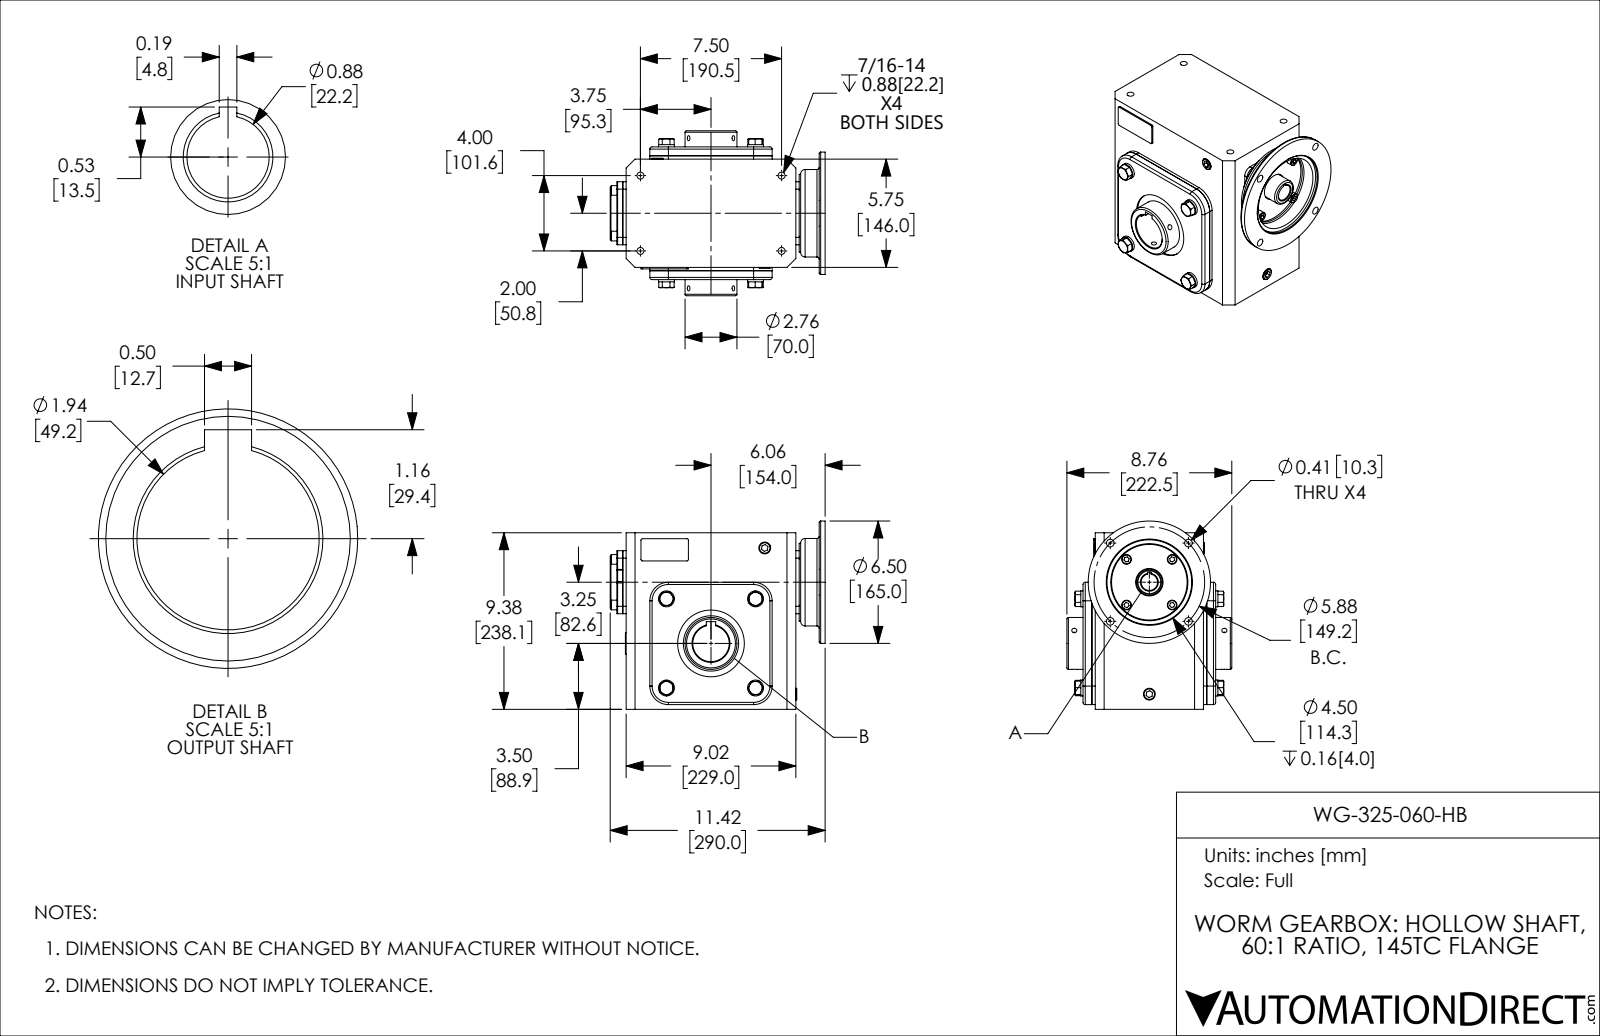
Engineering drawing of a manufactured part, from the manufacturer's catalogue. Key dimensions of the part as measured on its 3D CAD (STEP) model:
Part name (STEP PRODUCT): WG-325-060-HB
STEP written by: SolidWorks 2017 (AUTOMOTIVE_DESIGN)
Units: inches
Bodies: 39 solids, 587 faces (314 planar, 178 cylindrical, 95 other)
Overall size (bounding box): 11.417 × 9.998 × 8.76
Volume: 516.3 in³ · Surface area: 987.3 in²
Round holes (diameter × count): ⌀0.272 ×6, ⌀0.368 ×4, ⌀0.406 ×4, ⌀0.628 ×3, ⌀0.591 ×1, ⌀0.875 ×1, ⌀0.978 ×1, ⌀1.181 ×1, ⌀1.457 ×1, ⌀1.937 ×1, ⌀2.441 ×1, ⌀2.756 ×1
Round bosses / shafts (diameter × count): ⌀0.846 ×4, ⌀0.512 ×4, ⌀6.496 ×1, ⌀4.646 ×1, ⌀4.134 ×1, ⌀2.835 ×1, ⌀1.378 ×1, ⌀1.142 ×1
Partial cylindrical surfaces — rounded edges, fillets, slot ends (radius × count): R0.118 ×8, R0.079 ×7, R0.394 ×4, R0.906 ×4, R0.984 ×4, R0.02 ×2, R0.039 ×2
Main face-to-face distances: 0.079, 0.177, 6.496, 0.394, 0.571, 6.319, 5.925, 6.398, 0.65, 0.472
Hole centre spacings: 2.937, 4.154, 4.244, 7.064, 7.972, 2.385, 4, 4.389
